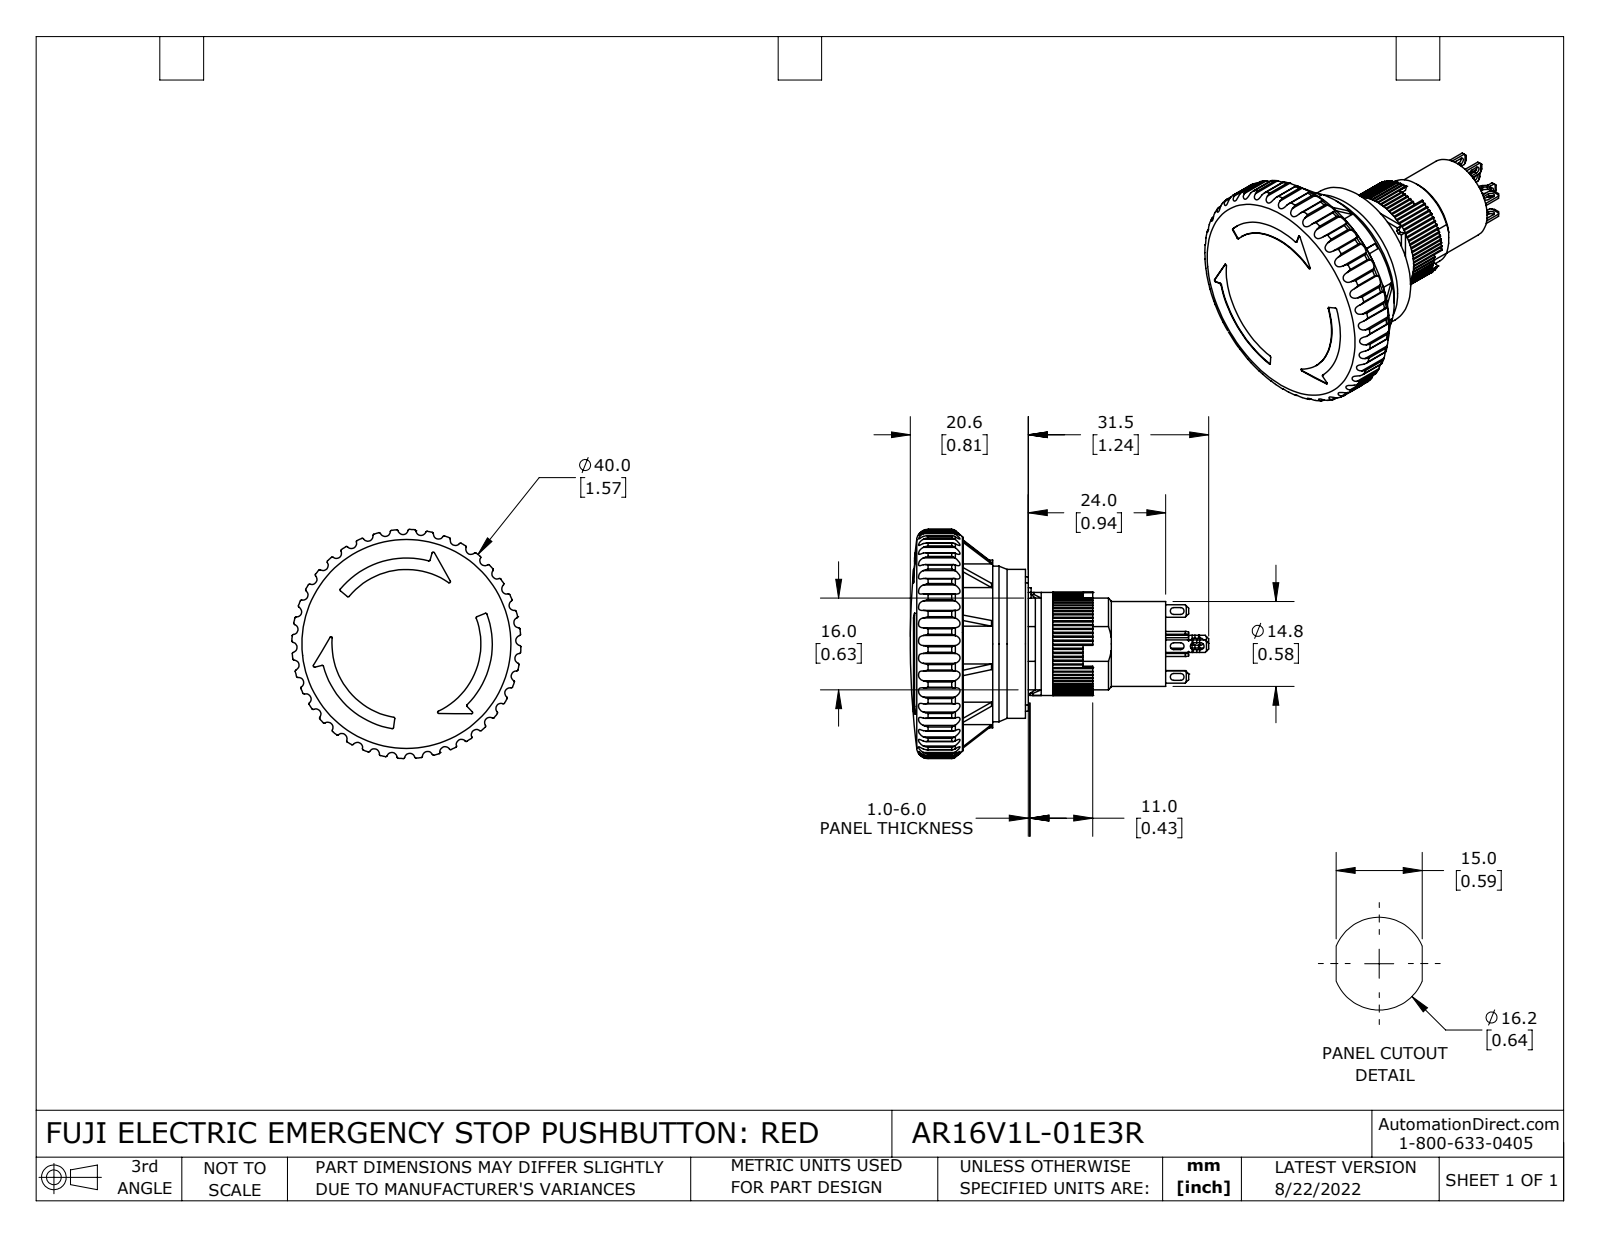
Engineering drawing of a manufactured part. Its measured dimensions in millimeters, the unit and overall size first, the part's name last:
Units: millimetres
Overall size (bounding box): 52.1 × 40 × 40
Round holes (diameter × count): ⌀14.8 ×1, ⌀16 ×1, ⌀18 ×1, ⌀27.2 ×1, ⌀36.4 ×1
Round bosses / shafts (diameter × count): ⌀29.3 ×1, ⌀26 ×1, ⌀21.8 ×1, ⌀6 ×1
Partial cylindrical surfaces — rounded edges, fillets, slot ends (radius × count): R0.2 ×80, R0.3 ×80, R0.9 ×40, R0.6 ×16, R0.5 ×8, R0.3 ×4, R0.7 ×4, R1 ×2
Main face-to-face distances: 1, 10.7, 13.5, 2.7, 0.5, 1.8, 21.7, 12.4, 2.3, 1.2
Volume: 15 800 mm³ · Surface area: 12 370 mm²
Bodies: 7 solids, 1081 faces (547 planar, 438 cylindrical, 96 other)
Part name (STEP PRODUCT): AR16V1L-01E3R
STEP written by: SolidWorks 2021 (CONFIG_CONTROL_DESIGN)
